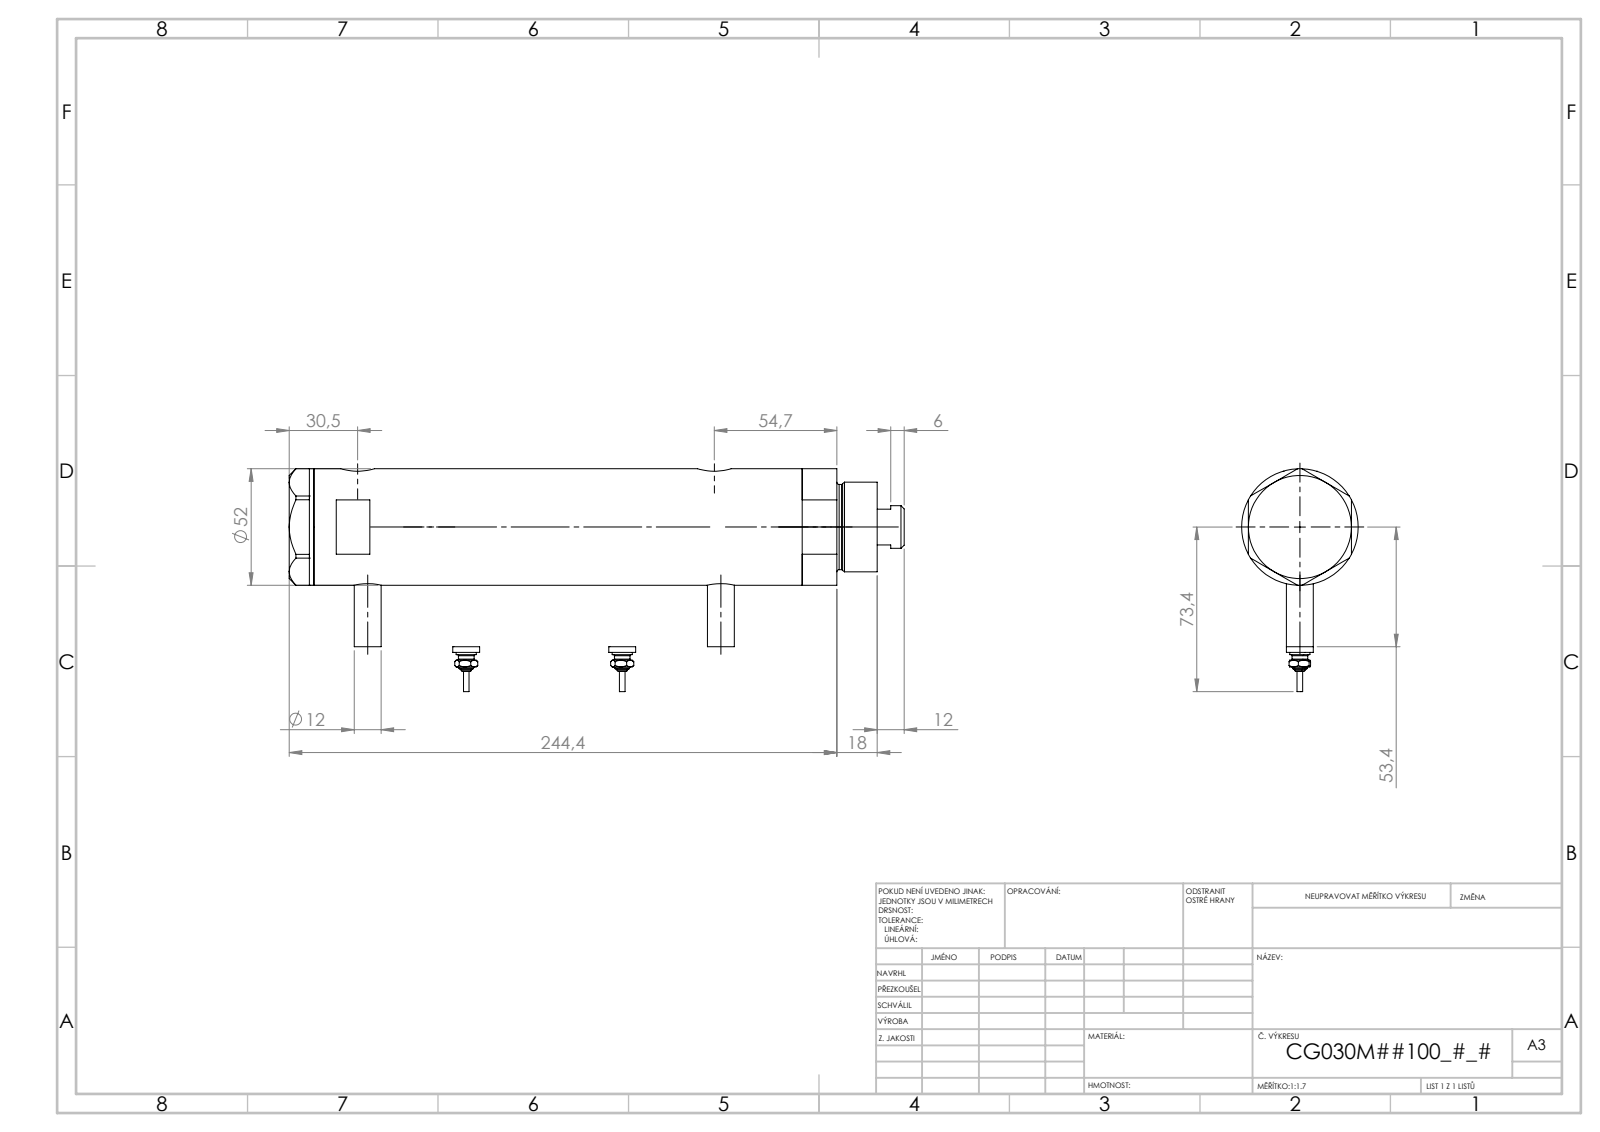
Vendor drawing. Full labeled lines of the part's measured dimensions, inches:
Part name (STEP PRODUCT): V270CG_VC; V270CG_SWITCH; V270CG_BACK; V270CG_FRONT (+1 more)
STEP written by: SolidWorks 2019 (CONFIG_CONTROL_DESIGN)
Units: inches
Bodies: 6 solids, 246 faces (95 planar, 77 cylindrical, 74 other)
Overall size (bounding box): 9.804 × 3.319 × 2.047
Volume: 27.06 in³ · Surface area: 153.6 in²
Round holes (diameter × count): ⌀0.197 ×2, ⌀0.383 ×2, ⌀0.492 ×2, ⌀0.591 ×2, ⌀0.256 ×1, ⌀0.787 ×1, ⌀0.846 ×1, ⌀1.181 ×1, ⌀1.299 ×1, ⌀1.732 ×1
Round bosses / shafts (diameter × count): ⌀0.472 ×3, ⌀0.354 ×2, ⌀0.276 ×2, ⌀0.171 ×2, ⌀0.094 ×2, ⌀2.047 ×1, ⌀1.575 ×1, ⌀1.496 ×1
Main face-to-face distances: 6.045, 0.937, 5.108, 0.433, 1.37, 6.478, 1.811, 7.911, 7.478, 6.541
Hole centre spacings: 0.114, 0.177, 4.99, 5.104, 5.167, 5.281, 0.114, 0.115
